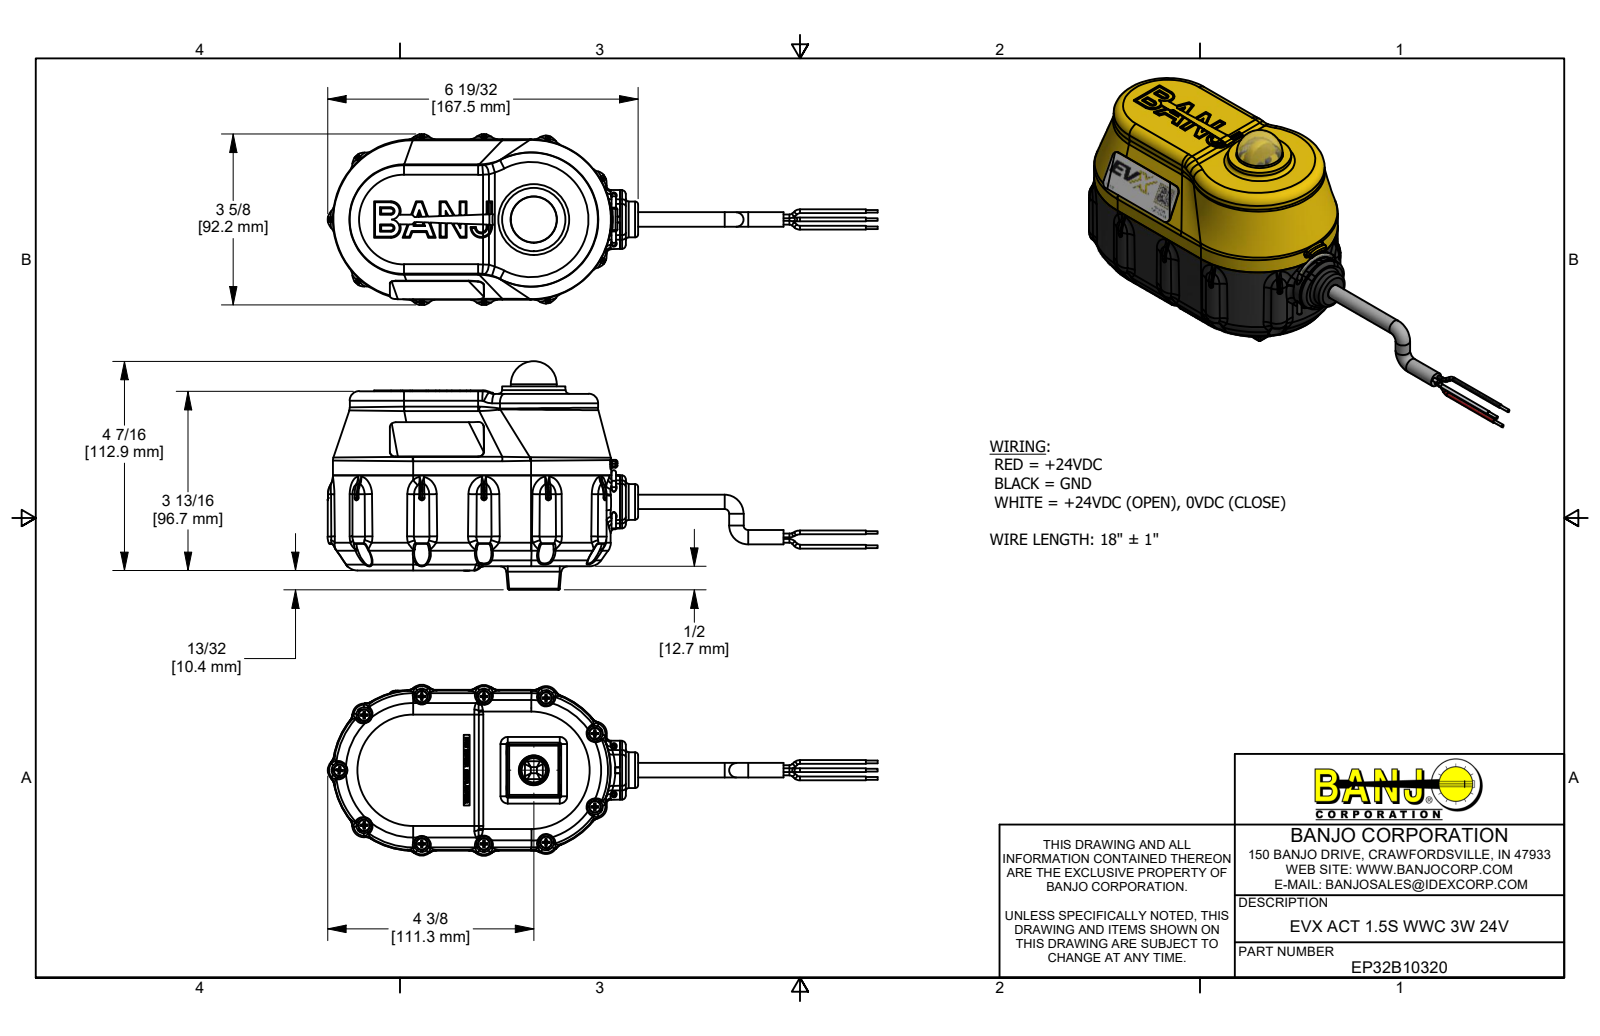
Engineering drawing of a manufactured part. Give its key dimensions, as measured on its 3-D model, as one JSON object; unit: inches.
{"part_name": "EP32B10320; B61905PPHS; B632038PM; EP10320 (+8 more)", "step_written_by": "Autodesk Inventor 2019 (AUTOMOTIVE_DESIGN)", "units": "inches", "bodies": {"solids": 73, "faces": 10037, "planar": 2572, "cylindrical": 2948, "other": 4517}, "overall_size": [11.685, 4.853, 3.63], "volume_in3": 31.17, "surface_area_in2": 405.1, "round_holes": [[0.095, 11], [0.15, 11], [0.08, 7], [0.107, 4], [0.126, 4], [0.136, 4], [0.148, 4], [0.15, 4], [0.17, 4], [0.105, 2], [0.118, 2], [0.123, 2]], "round_bosses_or_shafts": [[0.25, 17], [0.08, 15], [0.14, 11], [0.108, 11], [0.085, 11], [0.058, 6], [0.27, 4], [0.219, 4]], "partial_cylinders_radius": [[0.013, 180], [0.04, 145], [0.01, 92], [0.02, 71], [0.005, 55], [0.08, 28], [0.03, 26], [0.1, 22]], "face_to_face_distances": [0.1, 2.565, 0.06, 0.211, 0.151, 1.896, 1.836, 1.685, 0.569, 0.629], "hole_center_spacings": [1.283, 1.774, 2.69, 2.73, 3.789, 0.487, 0.668, 0.952]}
